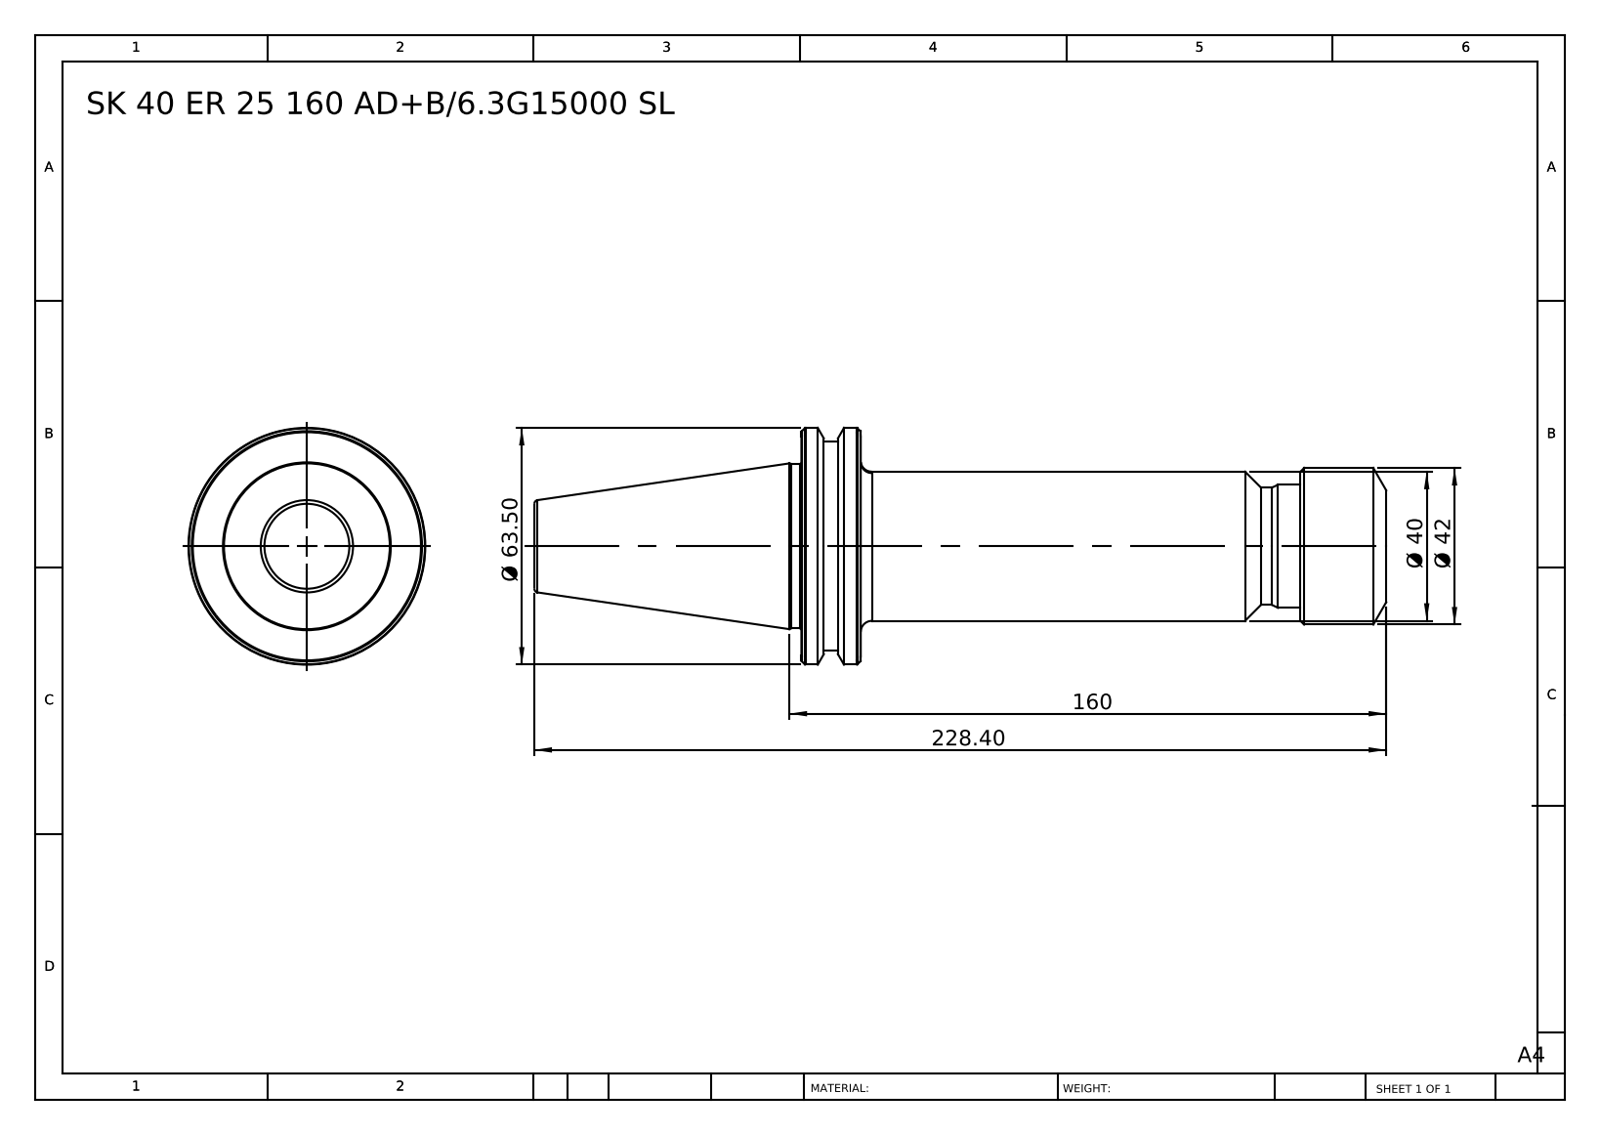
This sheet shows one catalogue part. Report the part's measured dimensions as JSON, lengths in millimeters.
{"part_name": "SK 40 ER 25 160 AD-6.3G15000 SL", "step_written_by": "SolidWorks 2014 (CONFIG_CONTROL_DESIGN)", "units": "millimeters", "bodies": {"solids": 1, "faces": 79, "planar": 7, "cylindrical": 16, "other": 56}, "overall_size": [228.4, 63.5, 63.5], "volume_mm3": 290472, "surface_area_mm2": 34757, "round_bosses_or_shafts": [[63.5, 1], [56, 1], [44, 1], [42, 1], [40, 1], [33, 1], [31.5, 1]], "face_to_face_distances": [15.9, 140.9, 156.8, 228.4, 87.5, 71.6, 23, 117.9, 133.8, 205.4]}
